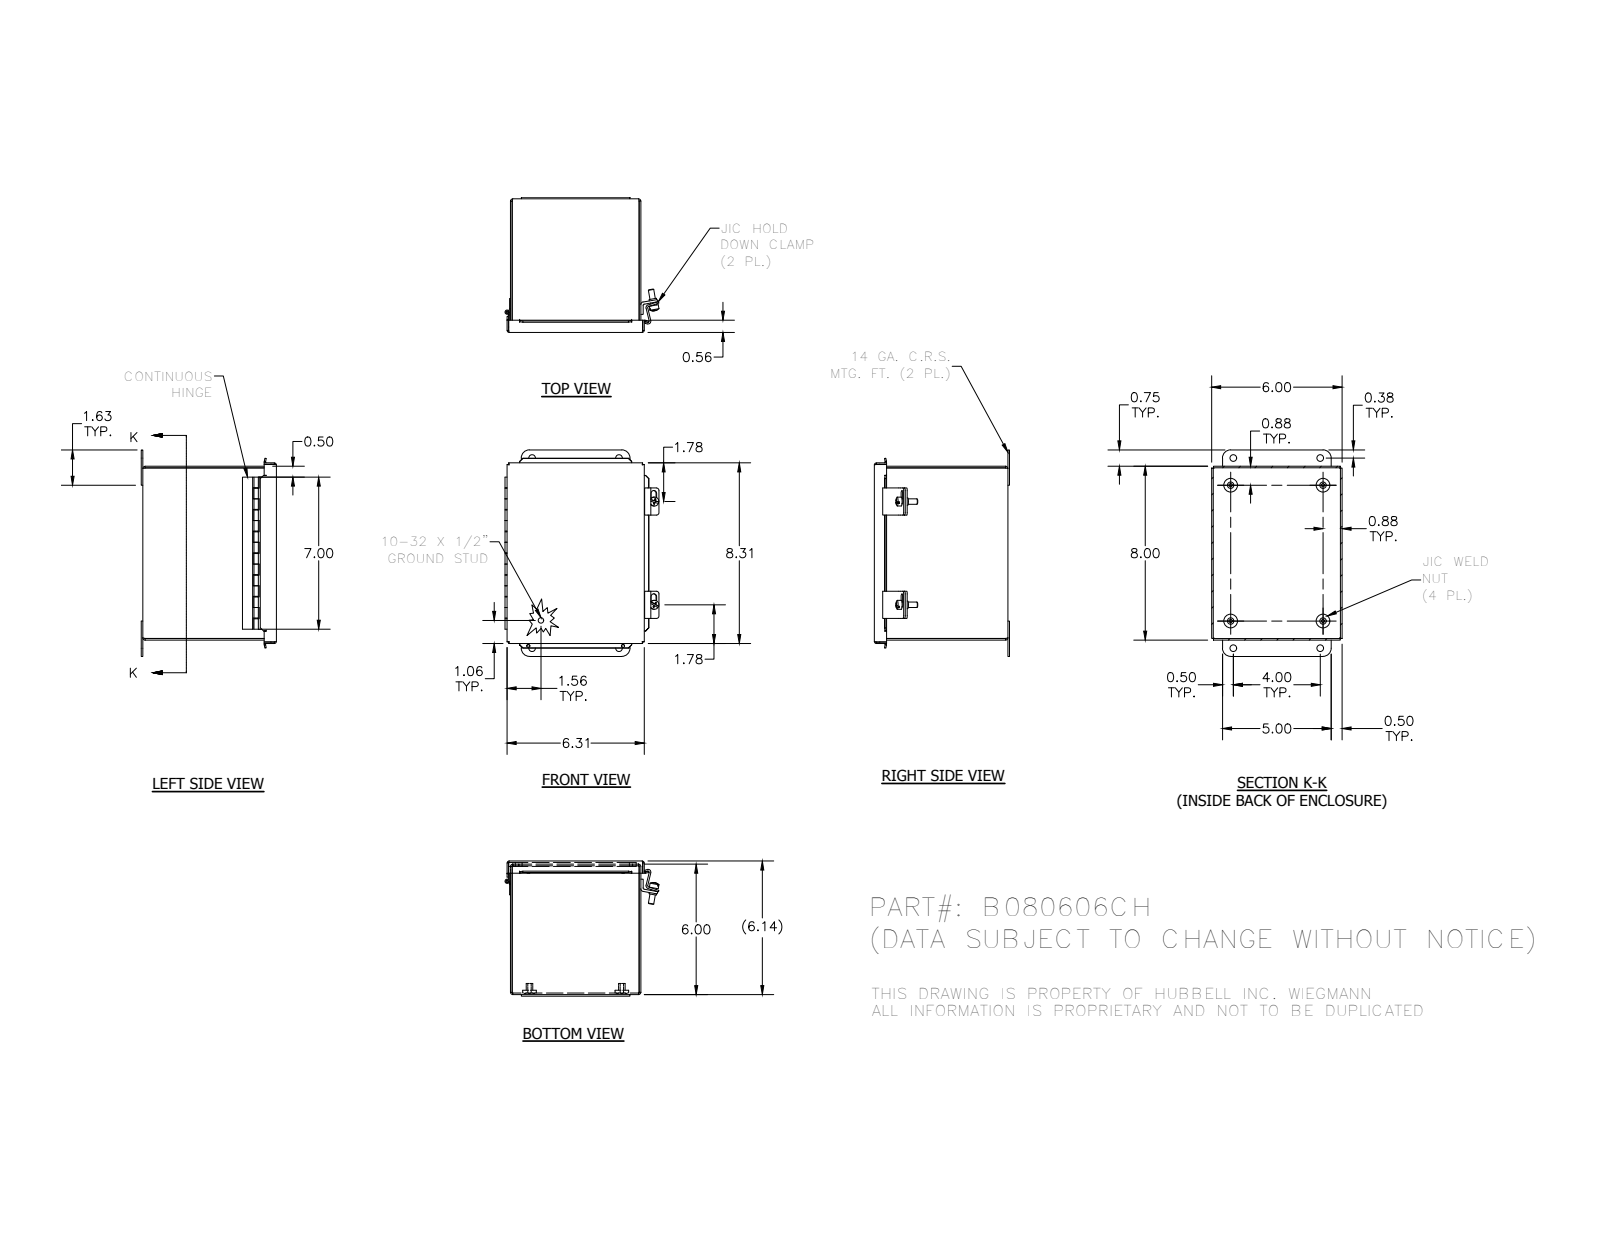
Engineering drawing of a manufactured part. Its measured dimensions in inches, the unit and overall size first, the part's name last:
Units: inches
Overall size (bounding box): 9.5 × 7.087 × 6.219
Round holes (diameter × count): ⌀0.156 ×4, ⌀0.31 ×4, ⌀0.14 ×2, ⌀0.196 ×2, ⌀0.116 ×1
Round bosses / shafts (diameter × count): ⌀0.625 ×4, ⌀0.3 ×4, ⌀0.25 ×3, ⌀0.41 ×2, ⌀0.344 ×2, ⌀0.2 ×1, ⌀0.19 ×1, ⌀0.1 ×1
Partial cylindrical surfaces — rounded edges, fillets, slot ends (radius × count): R0.031 ×15, R0.105 ×8, R0.125 ×8, R0.093 ×7, R0.133 ×4, R0.375 ×4, R0.063 ×3, R0.126 ×3
Main face-to-face distances: 0.074, 5.926, 7.926, 6.083, 6, 5.852, 0.062, 6.144, 6.009, 6.07
Hole centre spacings: 4.31, 1.256, 1.257, 4, 4.25, 7.501, 7.502, 7.558
Volume: 26.16 in³ · Surface area: 710.8 in²
Bodies: 20 solids, 459 faces (299 planar, 115 cylindrical, 45 other)
Part name (STEP PRODUCT): B080606CH; 3499; 3482; C1001 (+8 more)
STEP written by: Autodesk Inventor 2012 (AUTOMOTIVE_DESIGN)
